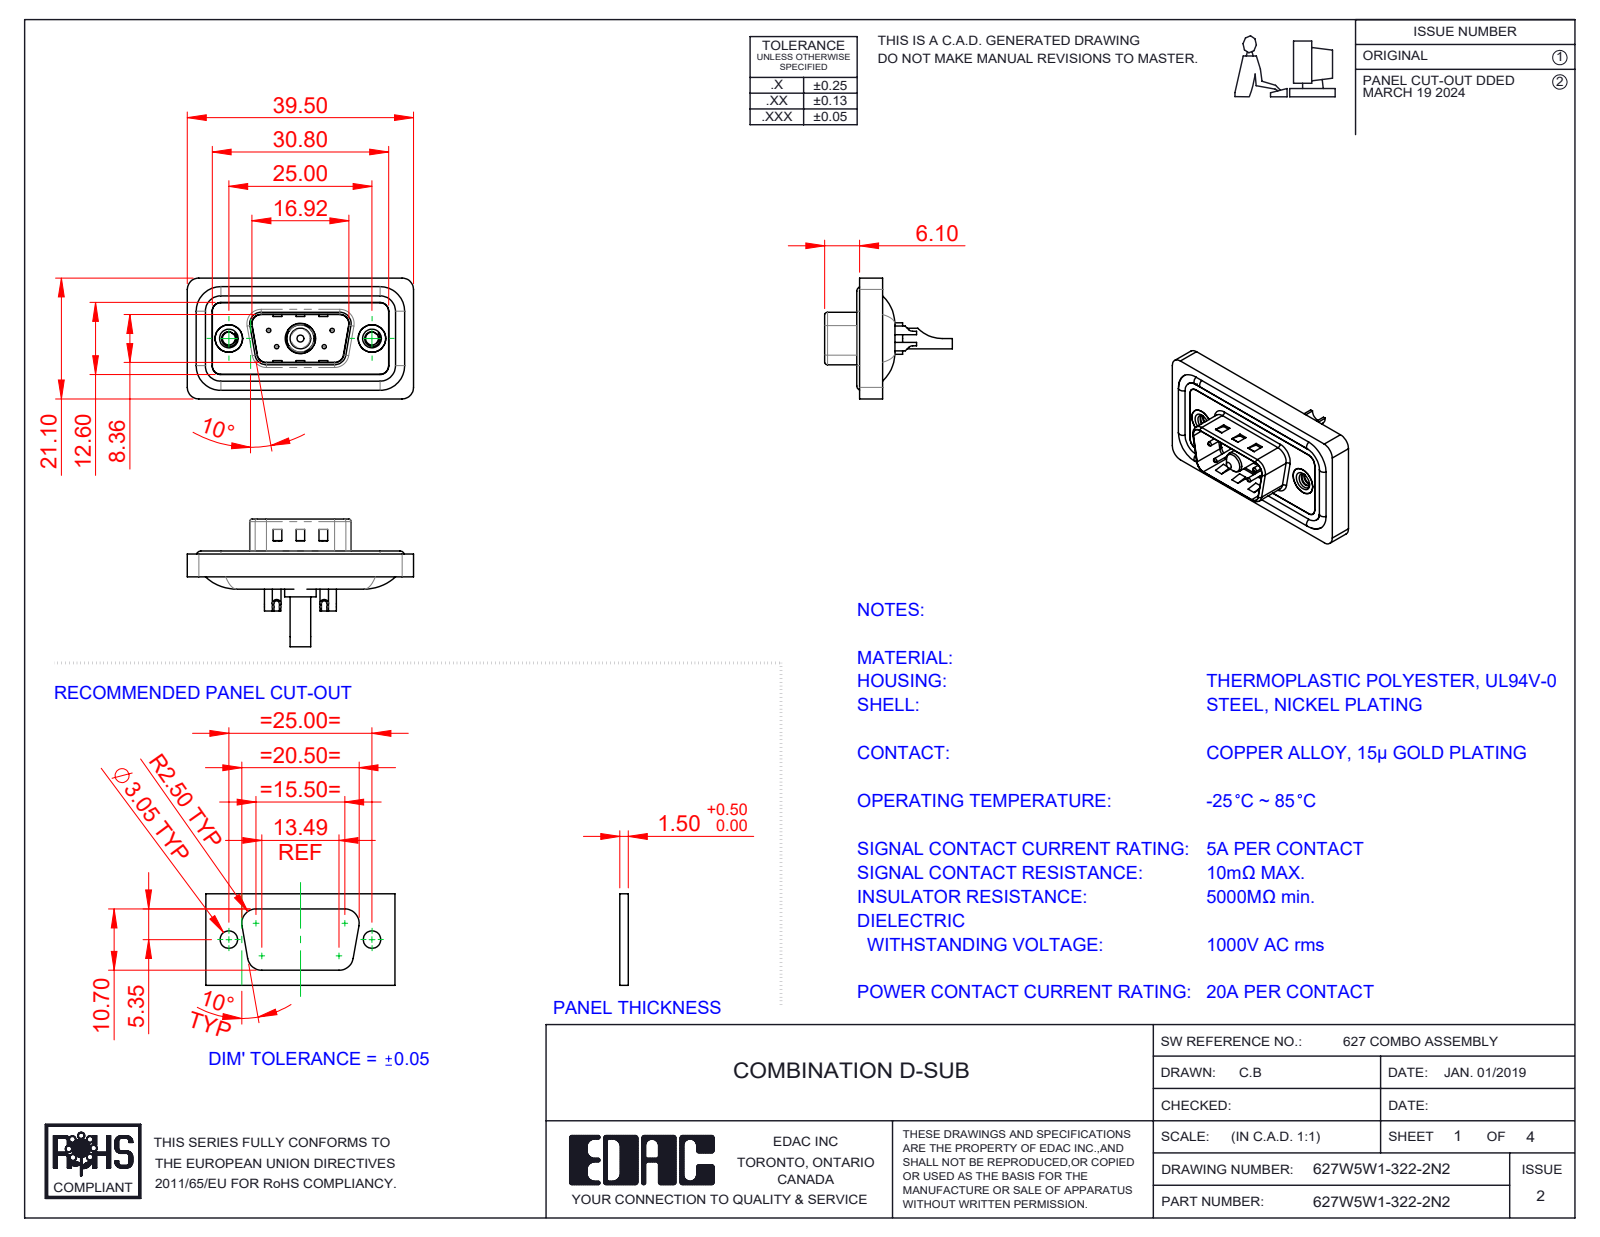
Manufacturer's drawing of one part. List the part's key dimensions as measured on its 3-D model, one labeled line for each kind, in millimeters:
Part name (STEP PRODUCT): 627Combo Contact Row 1_22; 627Combo Threaded Rivet_2; Power Pin_20A SC; 627W5W1-322-2N2 (+5 more)
STEP written by: SolidWorks 2023 (CONFIG_CONTROL_DESIGN)
Units: millimetres
Bodies: 13 solids, 605 faces (194 planar, 266 cylindrical, 145 other)
Overall size (bounding box): 39.5 × 22.3 × 21.1
Volume: 4 406 mm³ · Surface area: 7 056 mm²
Round holes (diameter × count): ⌀0.75 ×4, ⌀1 ×4, ⌀1.6 ×4, ⌀2 ×4, ⌀2.26 ×2, ⌀4 ×2, ⌀4.8 ×2, ⌀5 ×2, ⌀2.7 ×1, ⌀4.85 ×1, ⌀5.3 ×1
Round bosses / shafts (diameter × count): ⌀1.6 ×4, ⌀1.5 ×4, ⌀4.9 ×2, ⌀5.5 ×1, ⌀5.2 ×1, ⌀4.75 ×1, ⌀3.75 ×1, ⌀3.6 ×1
Partial cylindrical surfaces — rounded edges, fillets, slot ends (radius × count): R1.5 ×22, R2 ×18, R0.5 ×8, R1.6 ×8, R1 ×6, R0.25 ×4, R0.6 ×4, R0.65 ×4
Main face-to-face distances: 0.4, 1.1, 2.9, 1.6, 3.1, 0.5, 1.5, 2.5, 4, 0.8
Hole centre spacings: 3.16, 5.72, 7.1, 12.5, 18.1, 4.39, 4.4, 8.31
